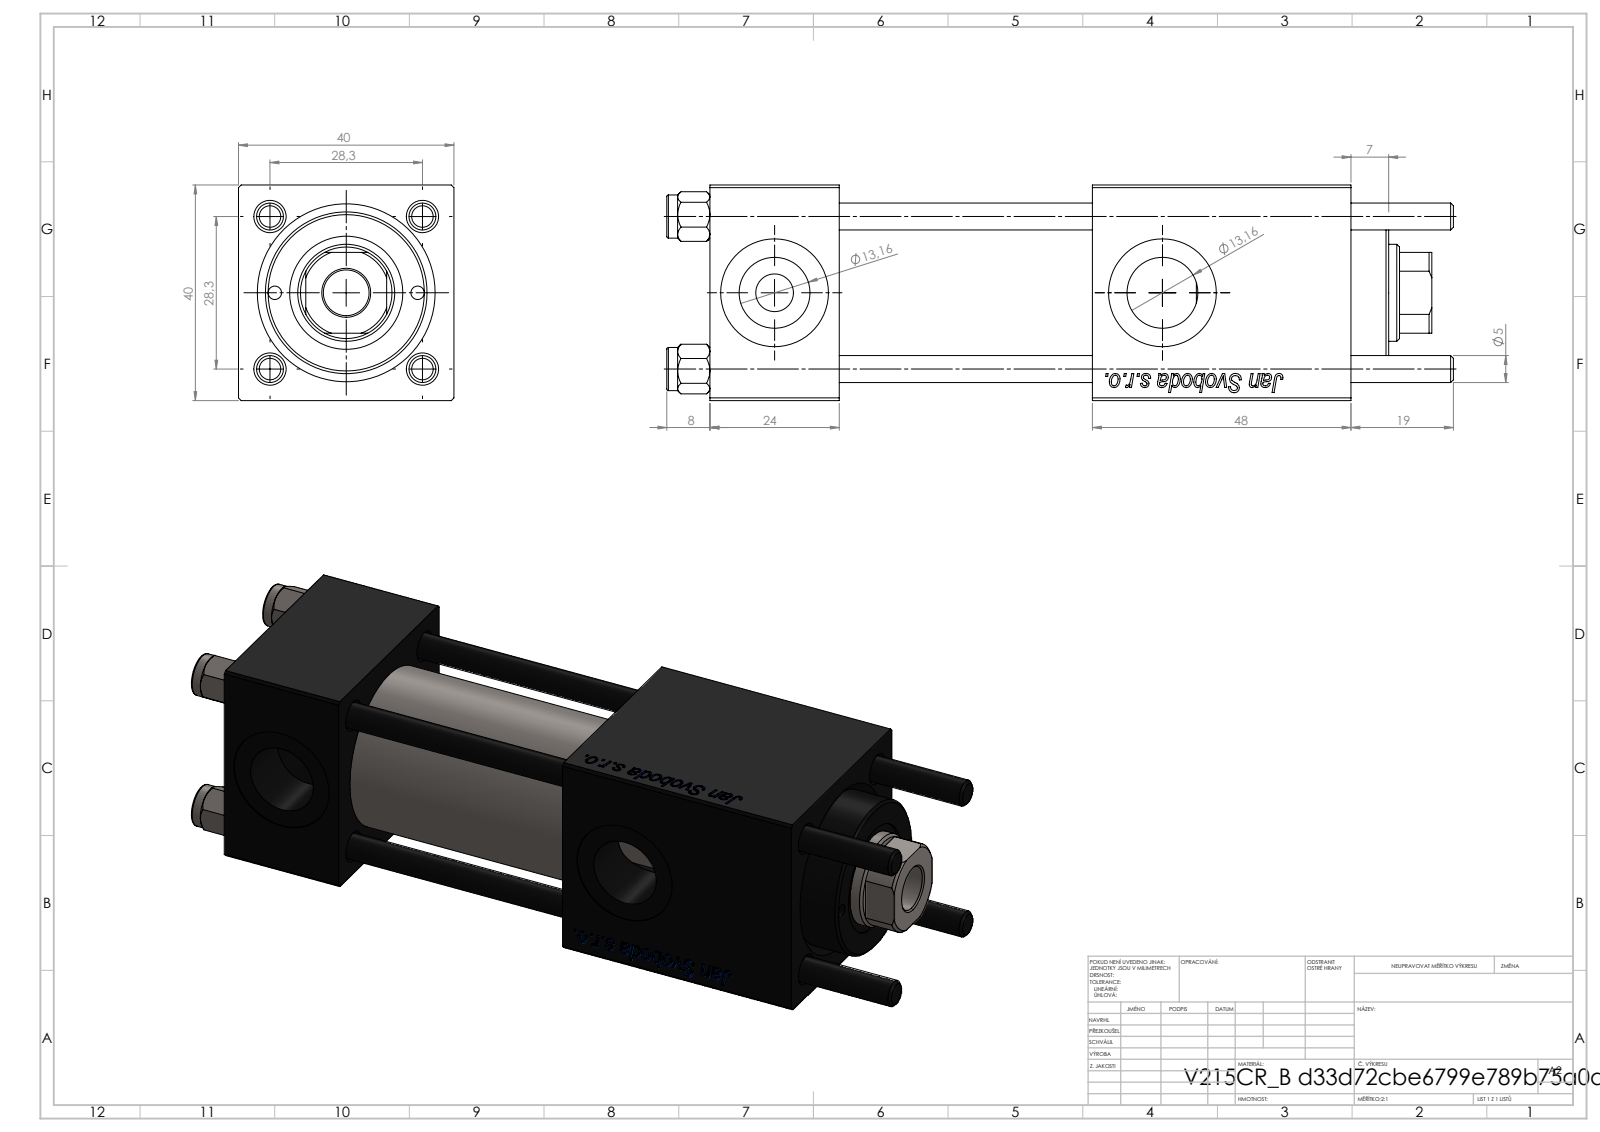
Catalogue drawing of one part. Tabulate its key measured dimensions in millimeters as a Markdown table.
| quantity | value |
| --- | --- |
| part name | V215CR_VCP_B; V215CR_B_TYCINKA; V215_VC_A; V215CR_B-1 (+1 more) |
| STEP written by | SolidWorks 2019 (CONFIG_CONTROL_DESIGN) |
| units | millimeters |
| bodies | 10 solids, 212 faces (60 planar, 44 cylindrical, 108 other) |
| overall size | 146 × 37.51 × 36.67 |
| volume | 61 221 mm³ |
| surface area | 25 687 mm² |
| round holes (diameter × count) | 5 × 4, 2.5 × 2, 8.5 × 1, 18 × 1, 21 × 1 |
| round bosses / shafts (diameter × count) | 8 × 4, 30 × 1, 25 × 1 |
| partial cylindrical surfaces (radius × count) | 8.5 × 1 |
| main face-to-face distances | 66.3, 8, 102, 35.7, 27, 39.3, 75, 134, 15, 110 |
| hole center spacings | 14.18, 20.01, 28.3, 30.84, 13.25, 40.02, 26.5 |
